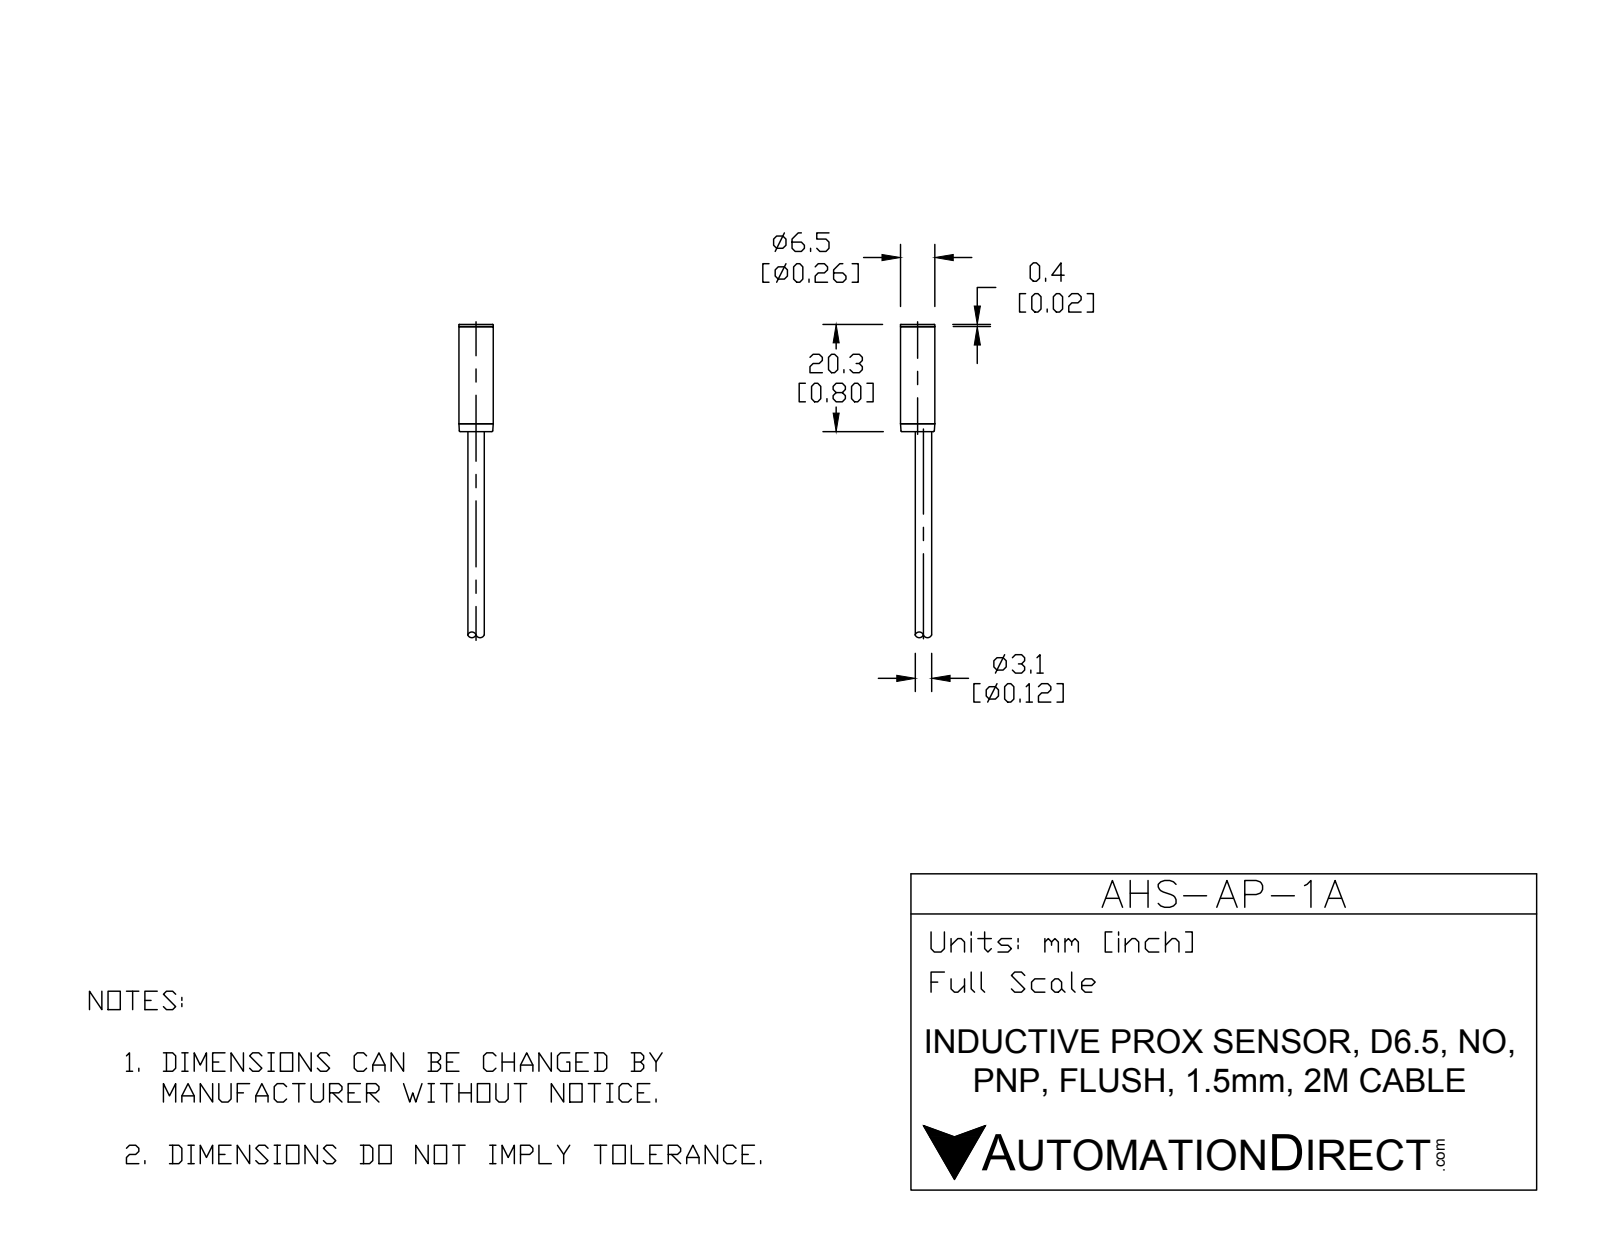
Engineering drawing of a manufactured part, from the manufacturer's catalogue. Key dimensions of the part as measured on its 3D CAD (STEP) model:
Part name (STEP PRODUCT): AHS-AP-1A
STEP written by: SolidWorks 2015 (CONFIG_CONTROL_DESIGN)
Units: millimetres
Bodies: 2 solids, 17 faces (5 planar, 6 cylindrical, 6 other)
Overall size (bounding box): 70.3 × 6.5 × 6.5
Volume: 1 050 mm³ · Surface area: 979 mm²
Round bosses / shafts (diameter × count): ⌀6.5 ×1, ⌀3.1 ×1
Main face-to-face distances: 20.3, 50, 70.3, 69.9, 19.9, 0.4
